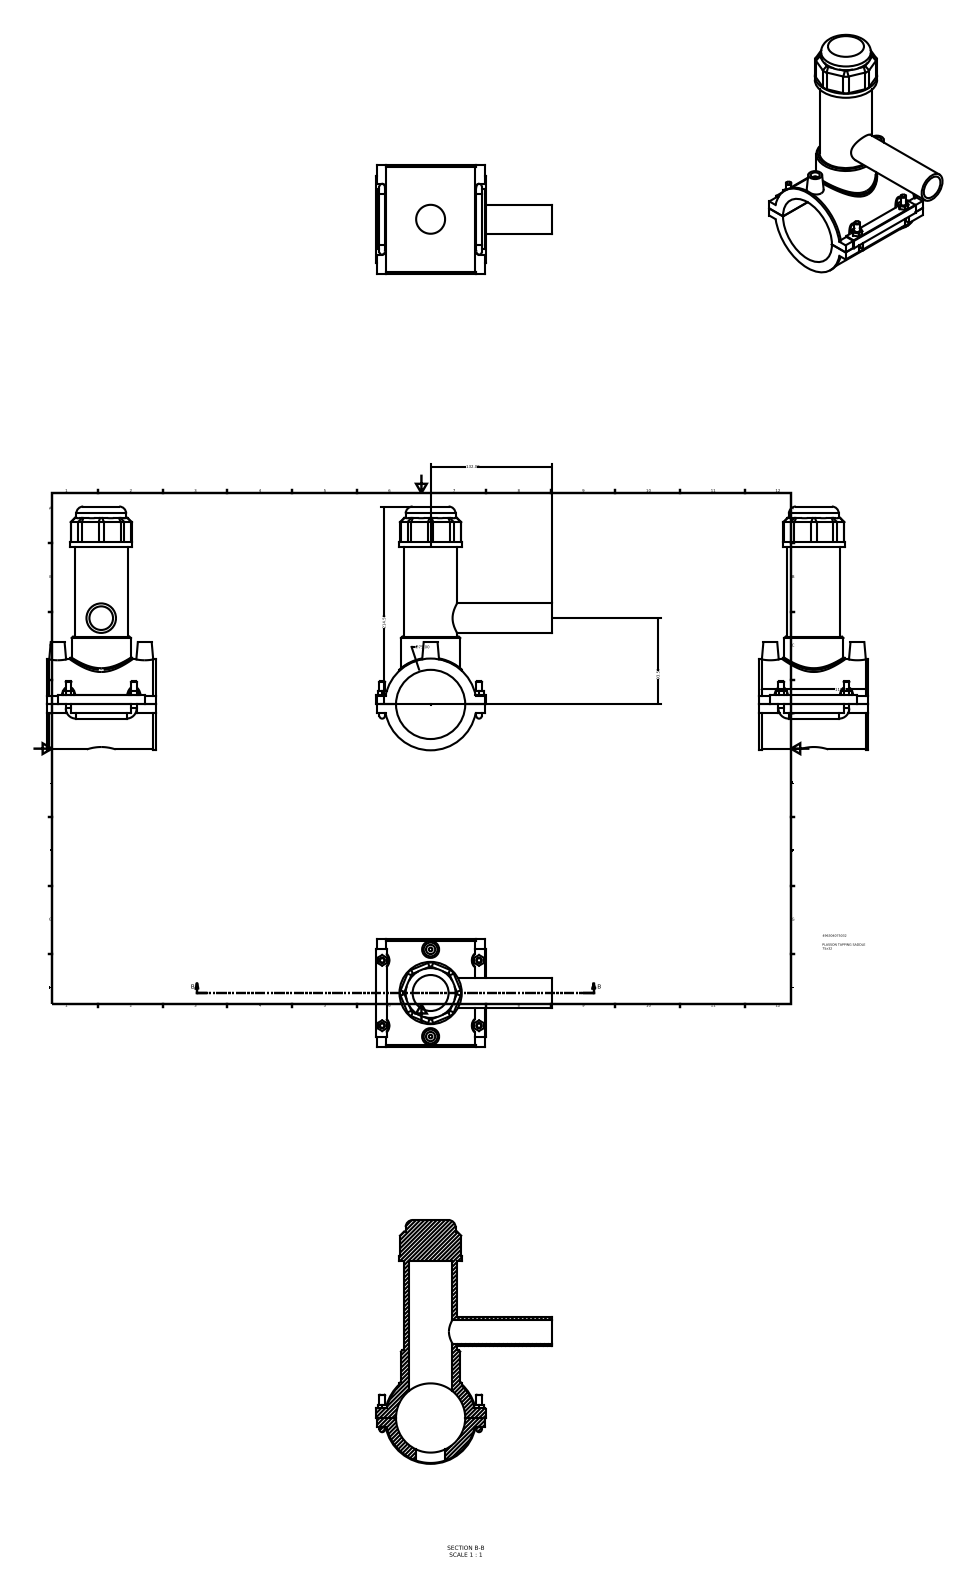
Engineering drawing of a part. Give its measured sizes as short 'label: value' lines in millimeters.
name: 496304075032
written by: Autodesk Inventor 2015 (AUTOMOTIVE_DESIGN)
unit: mm
bodies: 1 solid, 192 faces (118 planar, 49 cylindrical, 25 other)
size: 264.23 × 191.5 × 118
volume: 671 719 mm³; area: 165 562 mm²
holes: 2× ⌀10, 1× ⌀25.6, 1× ⌀31.36, 1× ⌀47.25, 1× ⌀75
bosses: 6× ⌀6, 2× ⌀4, 1× ⌀99.45, 1× ⌀97.5, 1× ⌀67.5, 1× ⌀64.12, 1× ⌀57.38, 1× ⌀54
rounds: 12× R7.5, 4× R3, 1× R0.5, 1× R50.7
face distances: 118, 170.3, 170.2, 9.33, 9.43, 1, 179.63, 19.76, 10.43, 10.33
hole spacings: 47.2, 94.4
